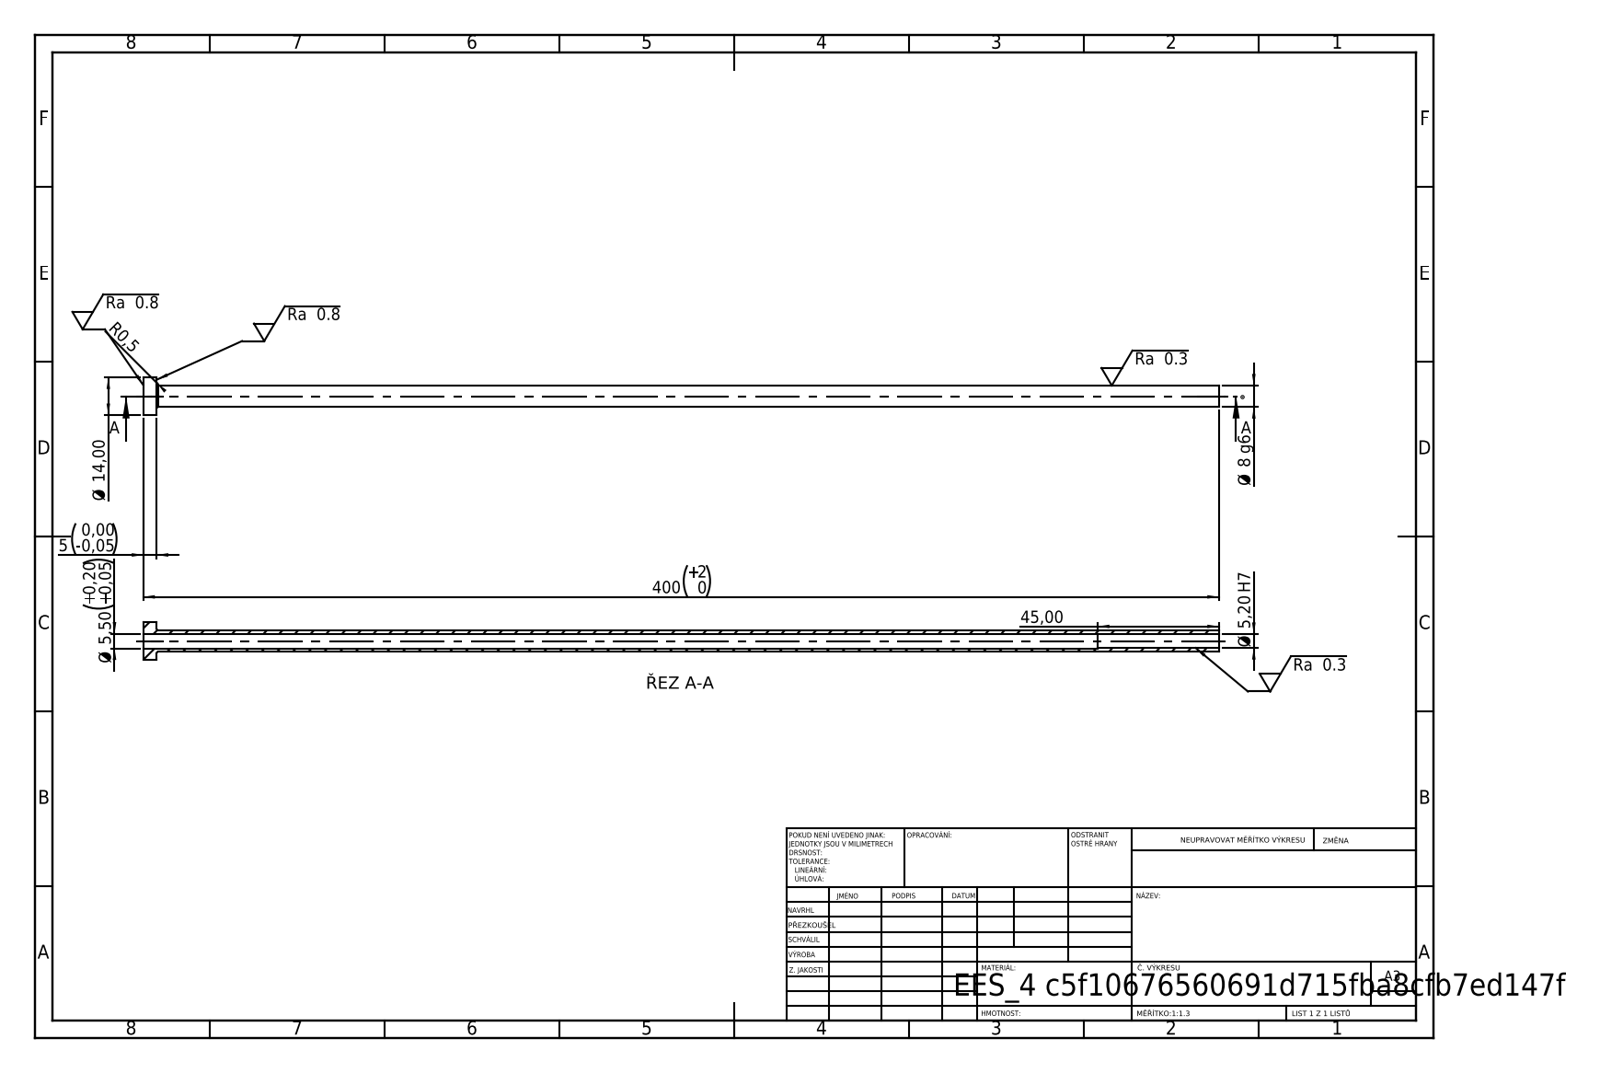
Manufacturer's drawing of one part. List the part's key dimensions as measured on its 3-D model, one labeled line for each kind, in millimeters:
STEP written by: SolidWorks 2019 (CONFIG_CONTROL_DESIGN)
Units: millimetres
Bodies: 1 solid, 14 faces (4 planar, 8 cylindrical, 2 other)
Overall size (bounding box): 400 × 14 × 14
Volume: 11 236 mm³ · Surface area: 17 277 mm²
Round holes (diameter × count): ⌀5.2 ×1, ⌀5.5 ×1
Round bosses / shafts (diameter × count): ⌀14 ×1, ⌀8 ×1
Main face-to-face distances: 5, 400, 395, 355, 350, 45
